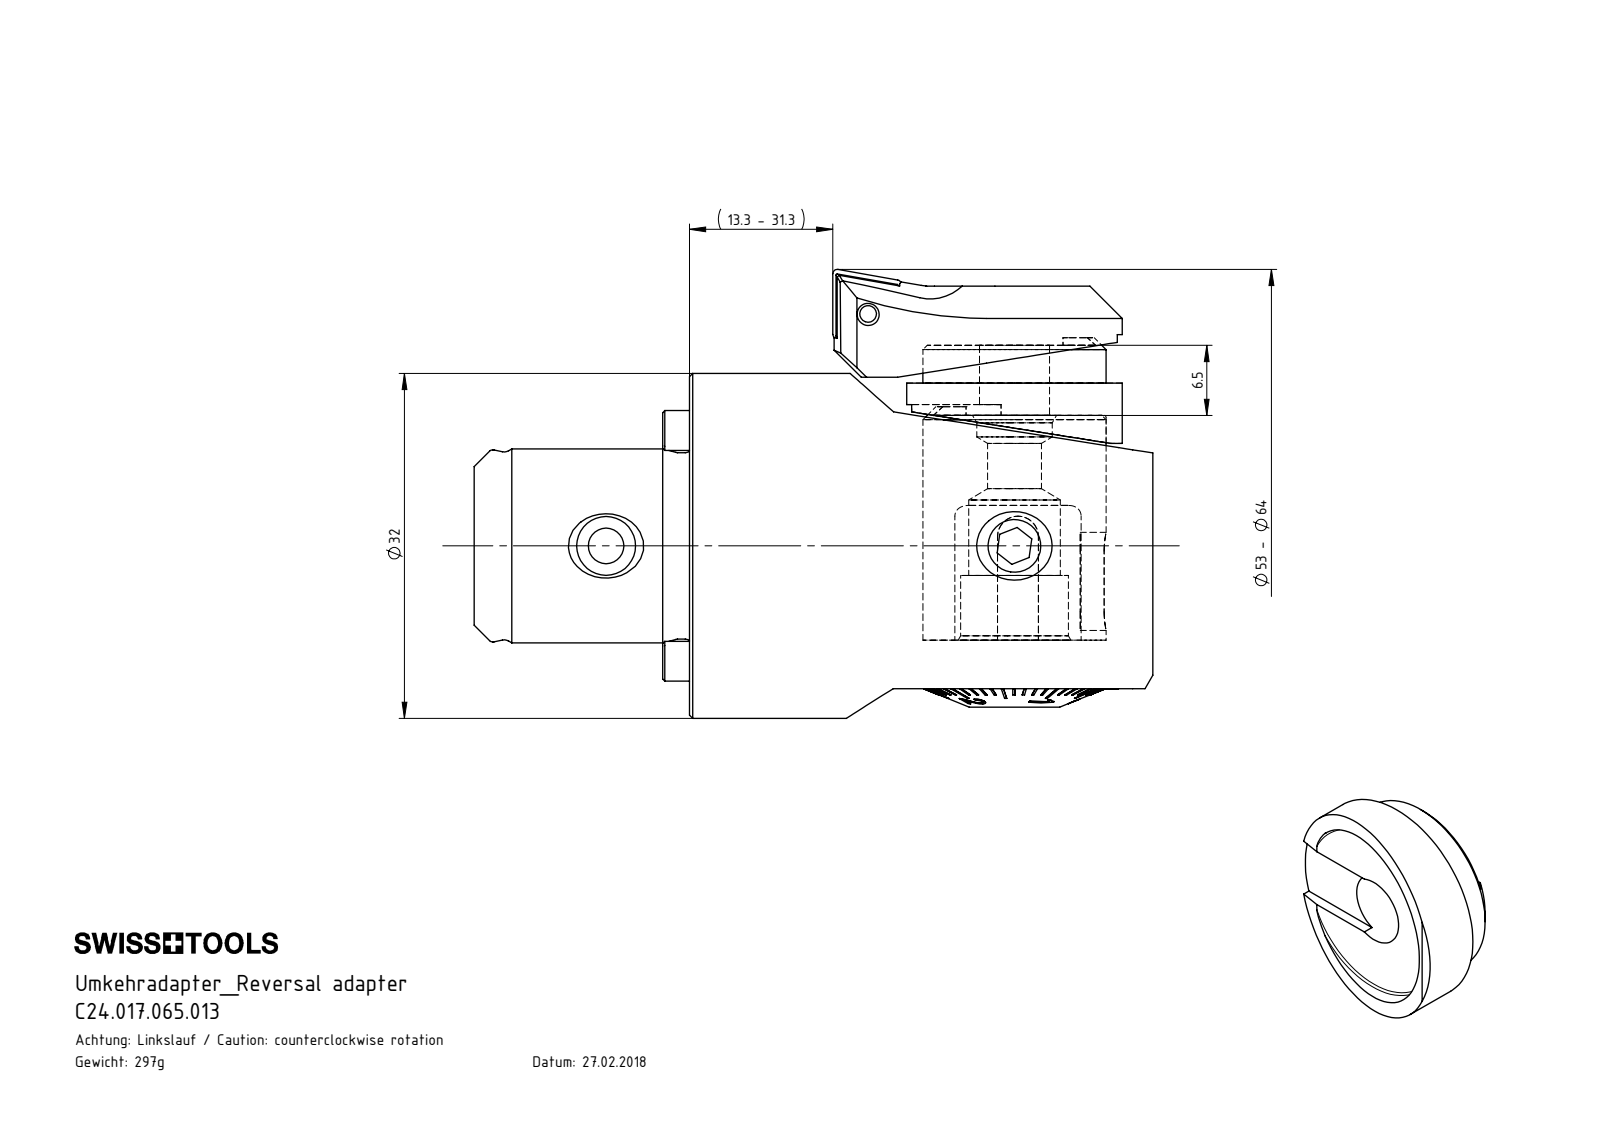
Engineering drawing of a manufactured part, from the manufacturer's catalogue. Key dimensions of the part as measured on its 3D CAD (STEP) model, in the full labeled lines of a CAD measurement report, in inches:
Part name (STEP PRODUCT): C24.017.065.013; F32-U00.001.006_B
STEP written by: SolidWorks 2017 (CONFIG_CONTROL_DESIGN)
Units: inches
Bodies: 1 solid, 28 faces (12 planar, 11 cylindrical, 5 other)
Overall size (bounding box): 0.787 × 0.787 × 0.386
Volume: 0.097 in³ · Surface area: 1.869 in²
Round holes (diameter × count): ⌀0.256 ×1, ⌀0.669 ×1
Round bosses / shafts (diameter × count): ⌀0.787 ×1
Partial cylindrical surfaces — rounded edges, fillets, slot ends (radius × count): R0.02 ×2
Main face-to-face distances: 0.256, 0.138, 0.118, 0.217, 0.079, 0.039, 0.028, 0.165, 0.244, 0.283
